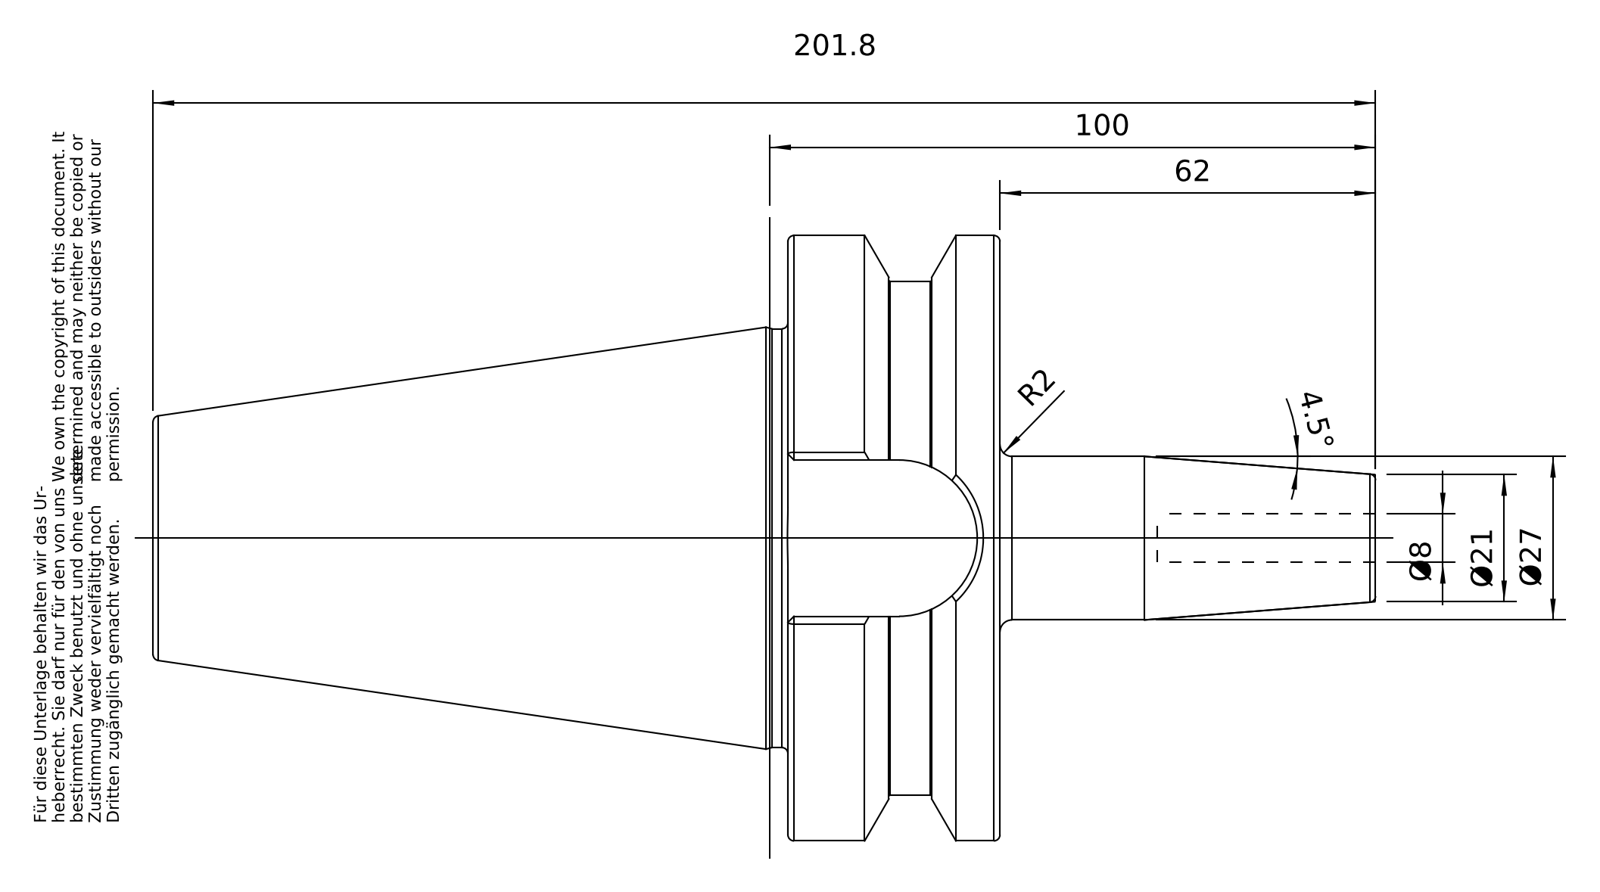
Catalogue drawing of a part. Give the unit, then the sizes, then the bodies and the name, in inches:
Units: inches
Overall size (bounding box): 7.945 × 3.936 × 3.936
Round holes (diameter × count): ⌀0.315 ×1, ⌀0.817 ×1, ⌀0.985 ×1, ⌀1.012 ×1
Round bosses / shafts (diameter × count): ⌀3.936 ×1, ⌀3.337 ×1, ⌀2.722 ×1, ⌀1.063 ×1, ⌀0.945 ×1
Partial cylindrical surfaces — rounded edges, fillets, slot ends (radius × count): R0.508 ×1
Main face-to-face distances: 1.378, 2.772, 4.126, 5.504, 1.016, 7.945, 3.819, 2.441, 1.89, 2.236
Volume: 30.35 in³ · Surface area: 88.88 in²
Bodies: 1 solid, 96 faces (26 planar, 22 cylindrical, 48 other)
Part name (STEP PRODUCT): 50-640-08
STEP written by: PRO/ENGINEER BY PARAMETRIC TECHNOLOGY CORPORATION, 2010430 (CONFIG_CONTROL_DESIGN)
